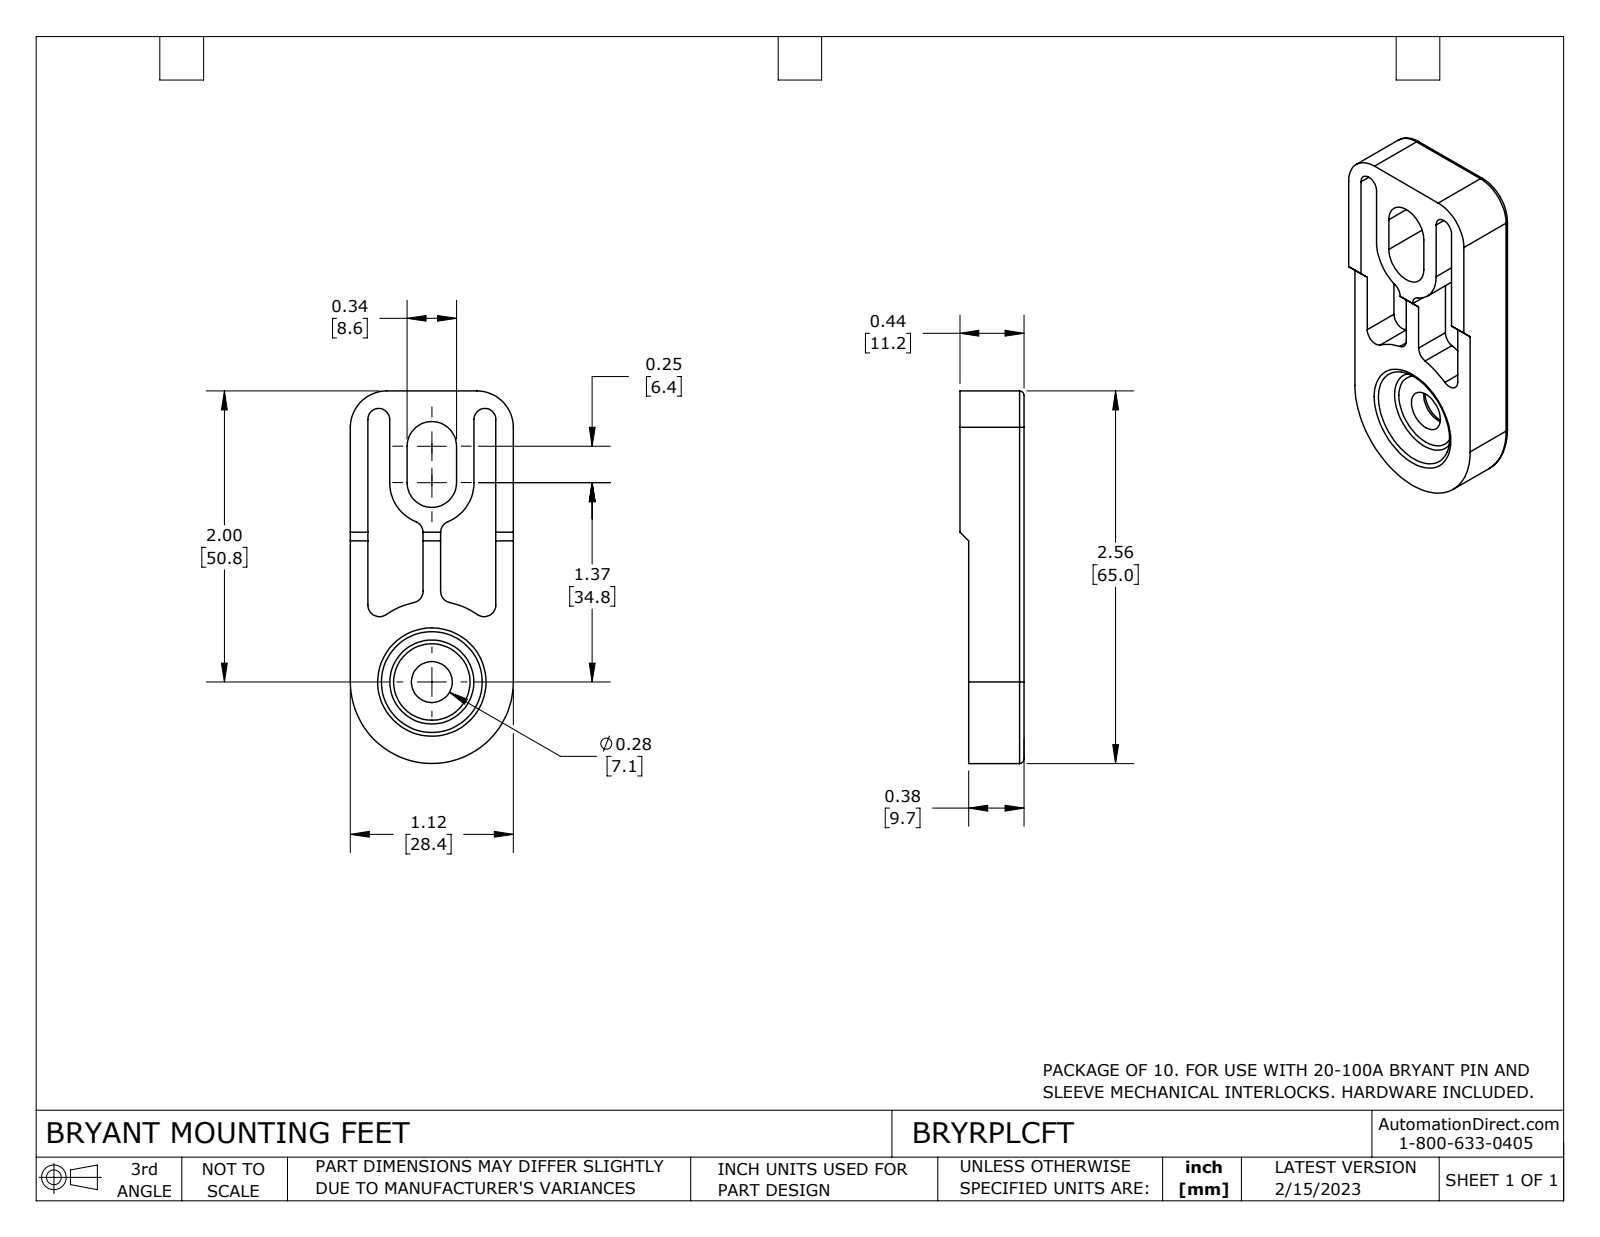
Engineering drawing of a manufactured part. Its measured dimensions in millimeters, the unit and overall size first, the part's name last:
Units: millimetres
Overall size (bounding box): 65 × 28.4 × 11.2
Round holes (diameter × count): ⌀7.1 ×1
Partial cylindrical surfaces — rounded edges, fillets, slot ends (radius × count): R0.4 ×24, R2 ×6, R0.8 ×3, R1.9 ×2, R4.3 ×2, R6.4 ×2, R7.4 ×1, R14.2 ×1
Main face-to-face distances: 3, 3, 9.7, 25.4, 6.6, 28.4, 1.5, 8.1, 11.2, 8.6
Volume: 11 600 mm³ · Surface area: 6 929 mm²
Bodies: 1 solid, 130 faces (37 planar, 59 cylindrical, 34 other)
Part name (STEP PRODUCT): BRYRPLCFT
STEP written by: SolidWorks 2021 (CONFIG_CONTROL_DESIGN)
